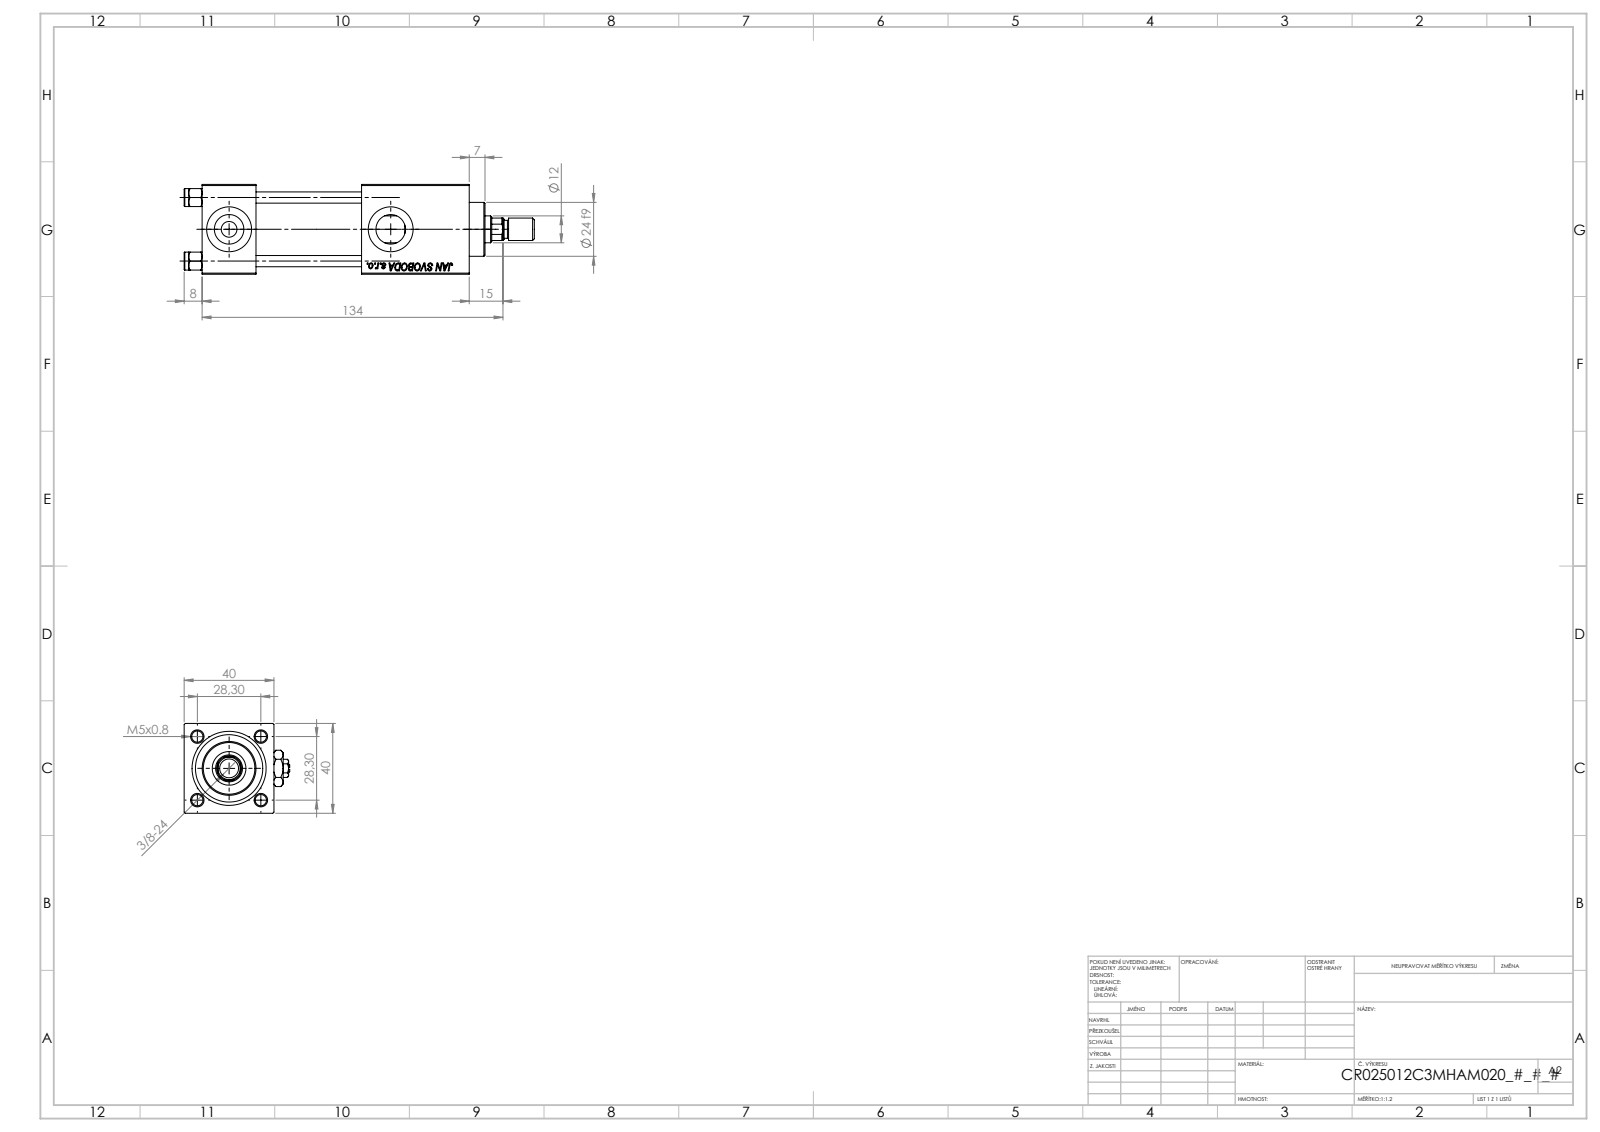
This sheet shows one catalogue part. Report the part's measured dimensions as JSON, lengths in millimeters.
{"part_name": "V215CR_VCP_C; ROD_END_AH; NUT_M5_C; V215_VC_A (+3 more)", "step_written_by": "SolidWorks 2019 (CONFIG_CONTROL_DESIGN)", "units": "millimeters", "bodies": {"solids": 14, "faces": 1262, "planar": 576, "cylindrical": 102, "other": 584}, "overall_size": [156, 47, 40], "volume_mm3": 142017, "surface_area_mm2": 56820, "round_holes": [[5, 4], [20, 3], [7, 2], [13.16, 2], [6.5, 1], [12, 1], [15, 1], [25, 1], [30, 1]], "round_bosses_or_shafts": [[8, 5], [31, 1], [24, 1], [10, 1]], "partial_cylinders_radius": [[5.5, 1]], "face_to_face_distances": [40, 24, 39.8, 48, 90.3, 66.3, 71, 47, 19.3, 119], "hole_center_spacings": [20.01, 28.3, 40.02, 72]}
